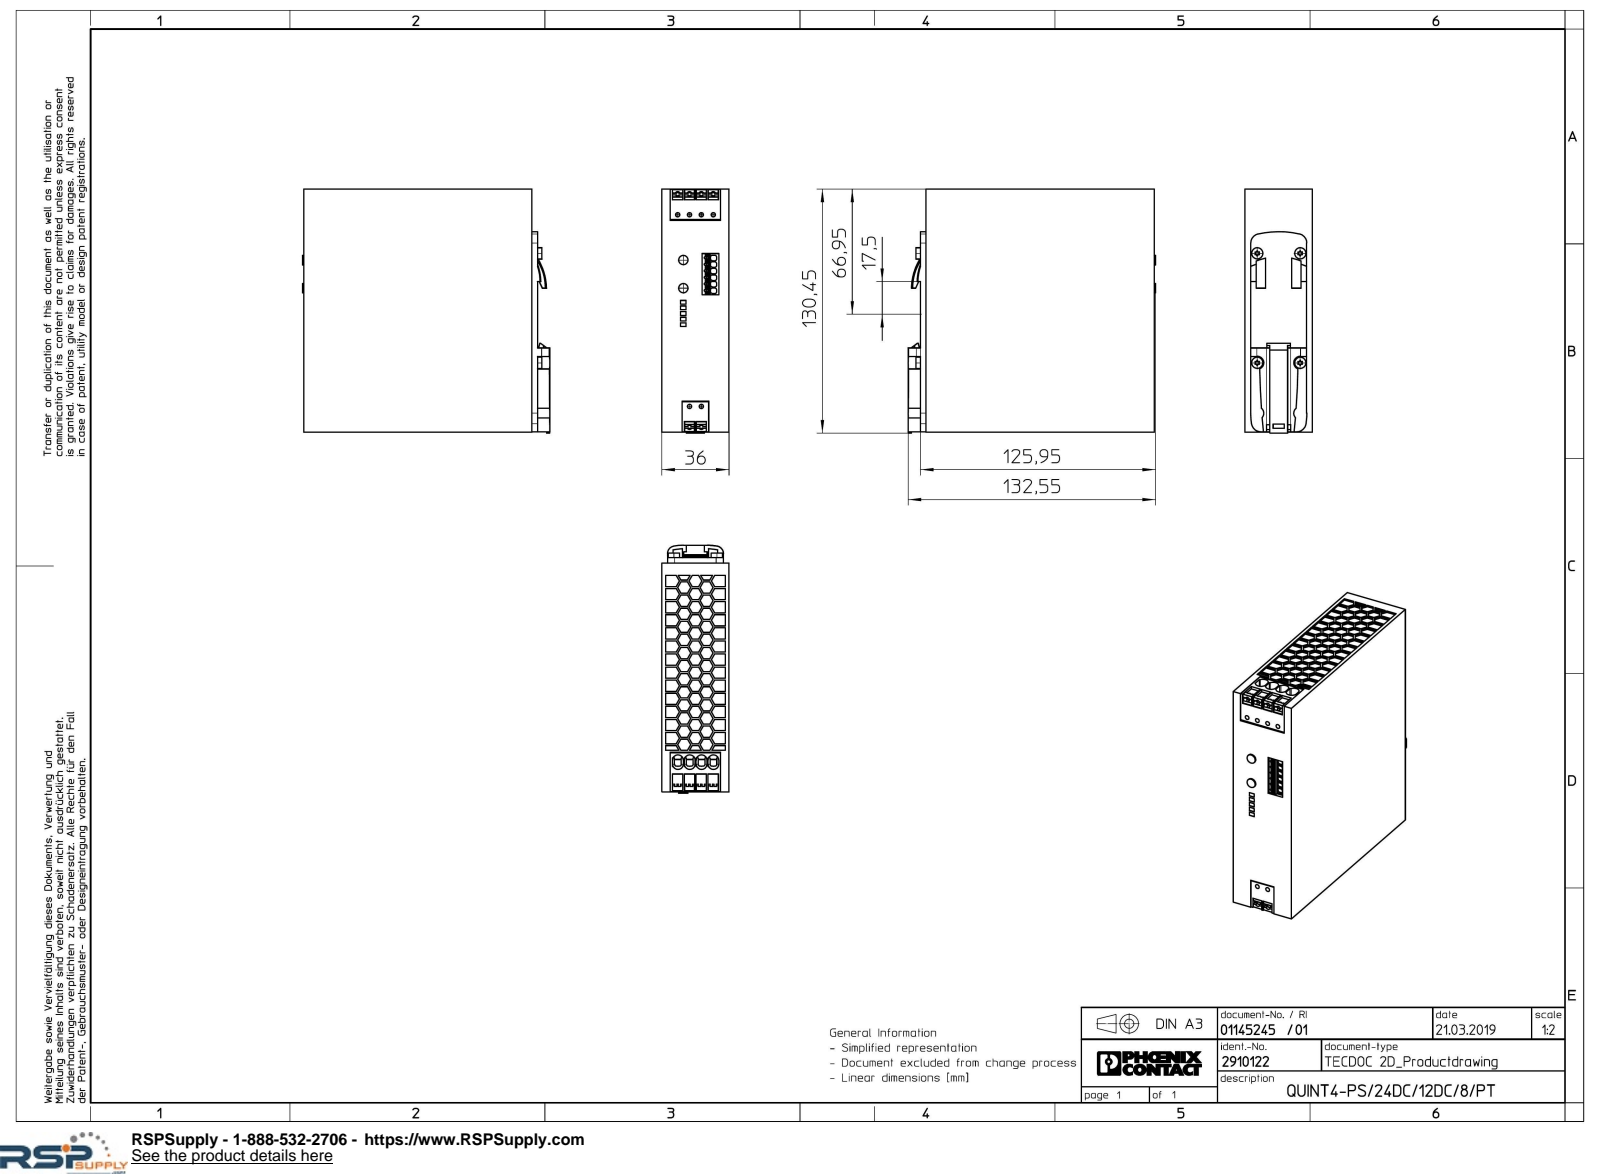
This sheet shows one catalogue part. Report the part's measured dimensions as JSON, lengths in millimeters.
{"part_name": "QUINT4_PS...DC...DC...PT-select", "step_written_by": "Creo Elements/Direct Modeling 20.1A 29-Sep-2018 (C) Parametric Technology GmbH (AUTOMOTIVE_DESIGN)", "units": "millimeters", "bodies": {"solids": 1, "faces": 1661, "planar": 1470, "cylindrical": 157, "other": 34}, "overall_size": [132.55, 130.45, 36], "volume_mm3": 581086, "surface_area_mm2": 57407, "round_holes": [[2.3, 6]], "round_bosses_or_shafts": [[6, 4], [5, 2]], "partial_cylinders_radius": [[0.1, 48], [0.97, 12], [1, 12], [1.1, 12], [2.9, 12], [0.57, 6], [0.6, 6], [3.5, 4]], "face_to_face_distances": [36, 0.8, 129.2, 128.4, 3, 125.25, 122.25, 130, 33, 9.5], "hole_center_spacings": [6.35, 102.7, 12.7, 102.5, 19.05, 103.28, 103.29]}
